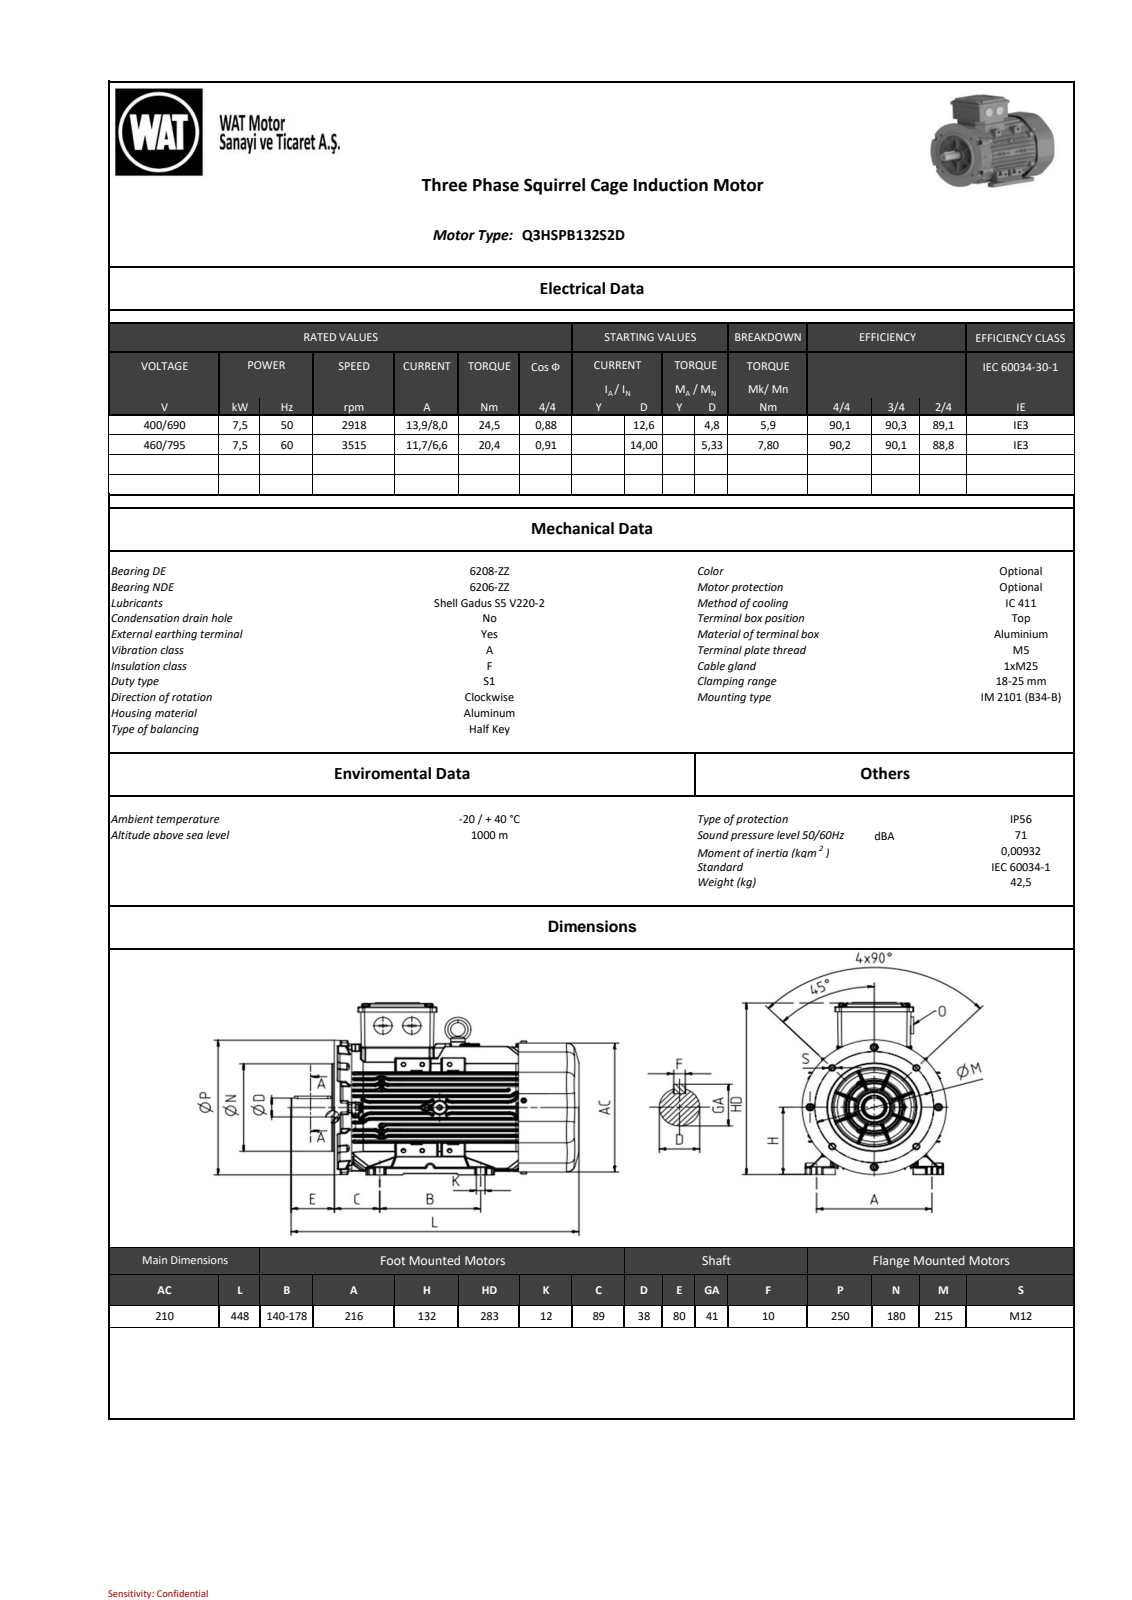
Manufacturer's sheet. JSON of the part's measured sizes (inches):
{"part_name": "Ar311510F80554ws", "step_written_by": "SIEMENS PLM Software NX 9.0 (AUTOMOTIVE_DESIGN)", "units": "inches", "bodies": {"solids": 0, "faces": 10852, "planar": 2250, "cylindrical": 3199, "other": 5403}, "overall_size": [17.614, 11.141, 9.865], "round_holes": [[0.472, 6], [0.406, 5], [0.327, 4], [0.262, 2], [1.094, 2], [0.157, 1], [0.186, 1], [0.315, 1], [0.512, 1], [2.26, 1], [2.31, 1], [9.488, 1]], "round_bosses_or_shafts": [[0.315, 12], [0.787, 4], [0.394, 4], [0.236, 4], [0.583, 3], [0.512, 3], [7.402, 1], [7.374, 1]], "partial_cylinders_radius": [[0.02, 708], [0.039, 615], [0.031, 542], [0.079, 236], [0.118, 41], [0.012, 12], [0.197, 12], [0.015, 9]], "face_to_face_distances": [0.039, 9.567, 0.197, 0.846, 1.416, 0.433, 3.919, 0.433, 0.983, 4.444], "hole_center_spacings": [4.232, 1.575, 5.985, 2.859, 4.331, 4.867, 5.669, 7.134]}
